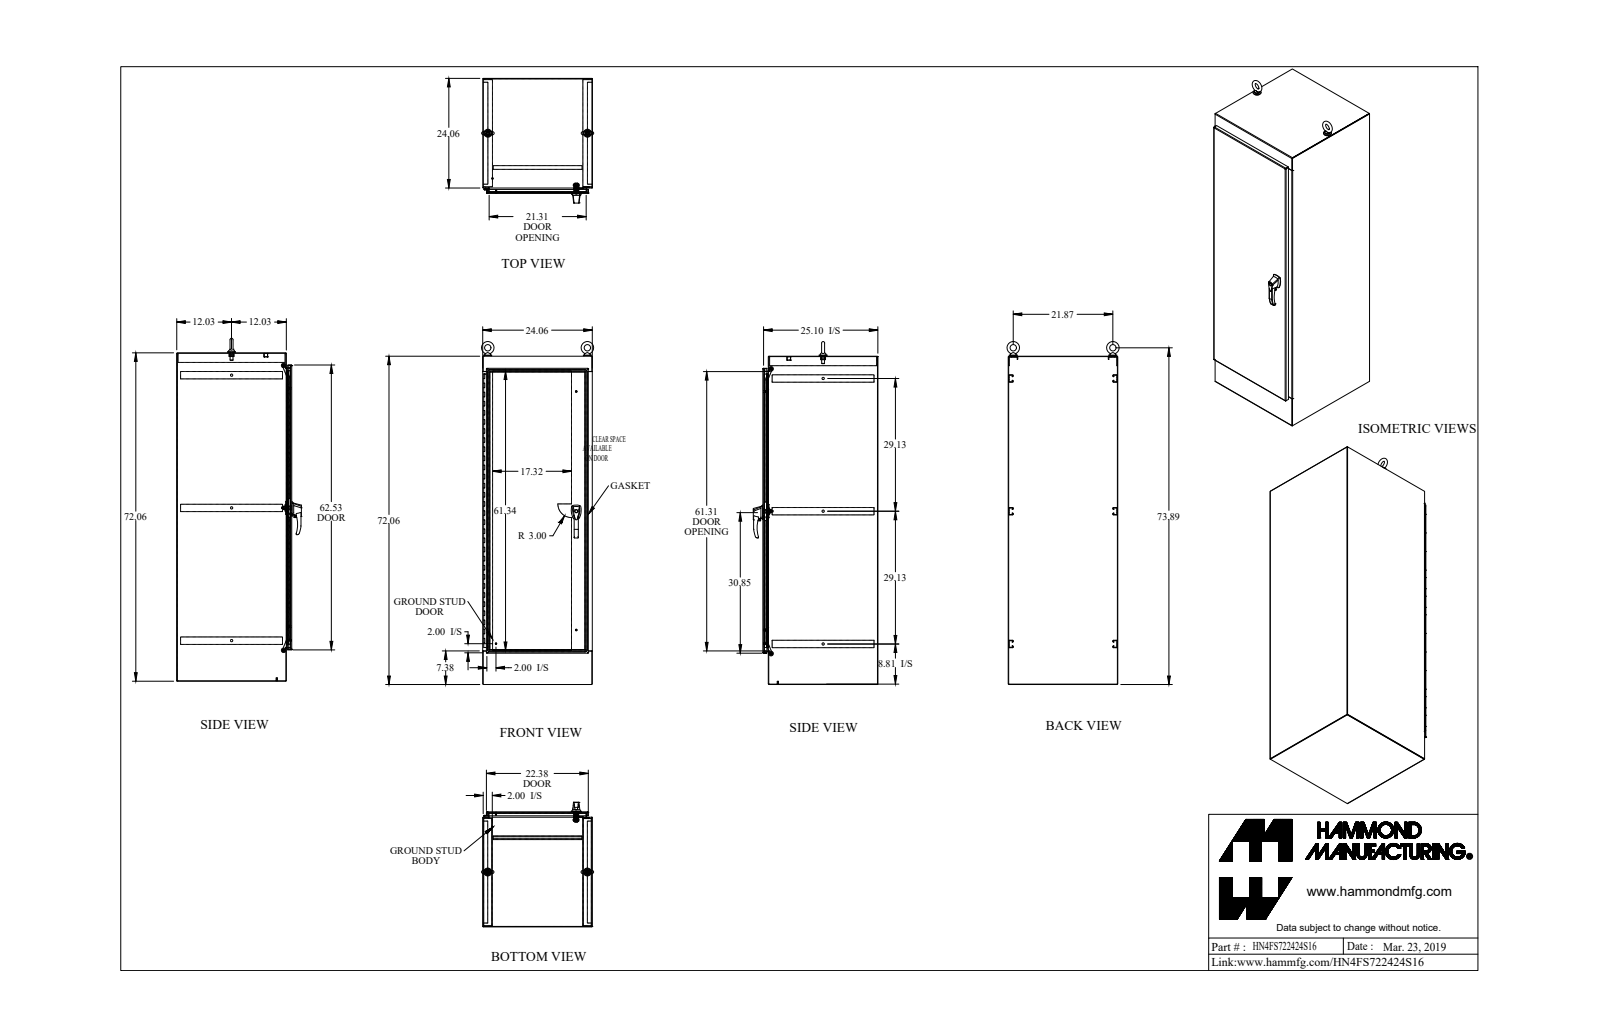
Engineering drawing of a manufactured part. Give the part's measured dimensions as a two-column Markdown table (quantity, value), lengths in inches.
| quantity | value |
| --- | --- |
| part name | HN4FS722424S16 |
| STEP written by | SolidWorks 2018 (AUTOMOTIVE_DESIGN) |
| units | inches |
| bodies | 56 solids, 1875 faces (862 planar, 848 cylindrical, 165 other) |
| overall size | 75.256 × 27.362 × 24.604 |
| volume | 952.9 in³ |
| surface area | 19 992 in² |
| round holes (diameter × count) | 0.304 × 10, 0.35 × 7, 0.5 × 3, 0.25 × 2, 0.257 × 2, 0.28 × 2, 0.281 × 2, 0.313 × 2, 0.39 × 2, 0.413 × 2, 0.527 × 2, 0.68 × 2 |
| round bosses / shafts (diameter × count) | 1.75 × 2, 1.5 × 2, 1.25 × 2, 1 × 2, 0.75 × 2, 0.738 × 2, 0.63 × 2, 0.625 × 2 |
| partial cylindrical surfaces (radius × count) | 0.043 × 42, 0.138 × 36, 0.5 × 23, 0.125 × 22, 0.017 × 16, 0.06 × 15, 0.048 × 13, 0.143 × 13 |
| main face-to-face distances | 0.095, 23.965, 25.152, 23.87, 24.06, 25.057, 25.247, 71.965, 1.187, 71.87 |
| hole center spacings | 6, 12, 18, 24, 30, 36, 42, 0.015 |
